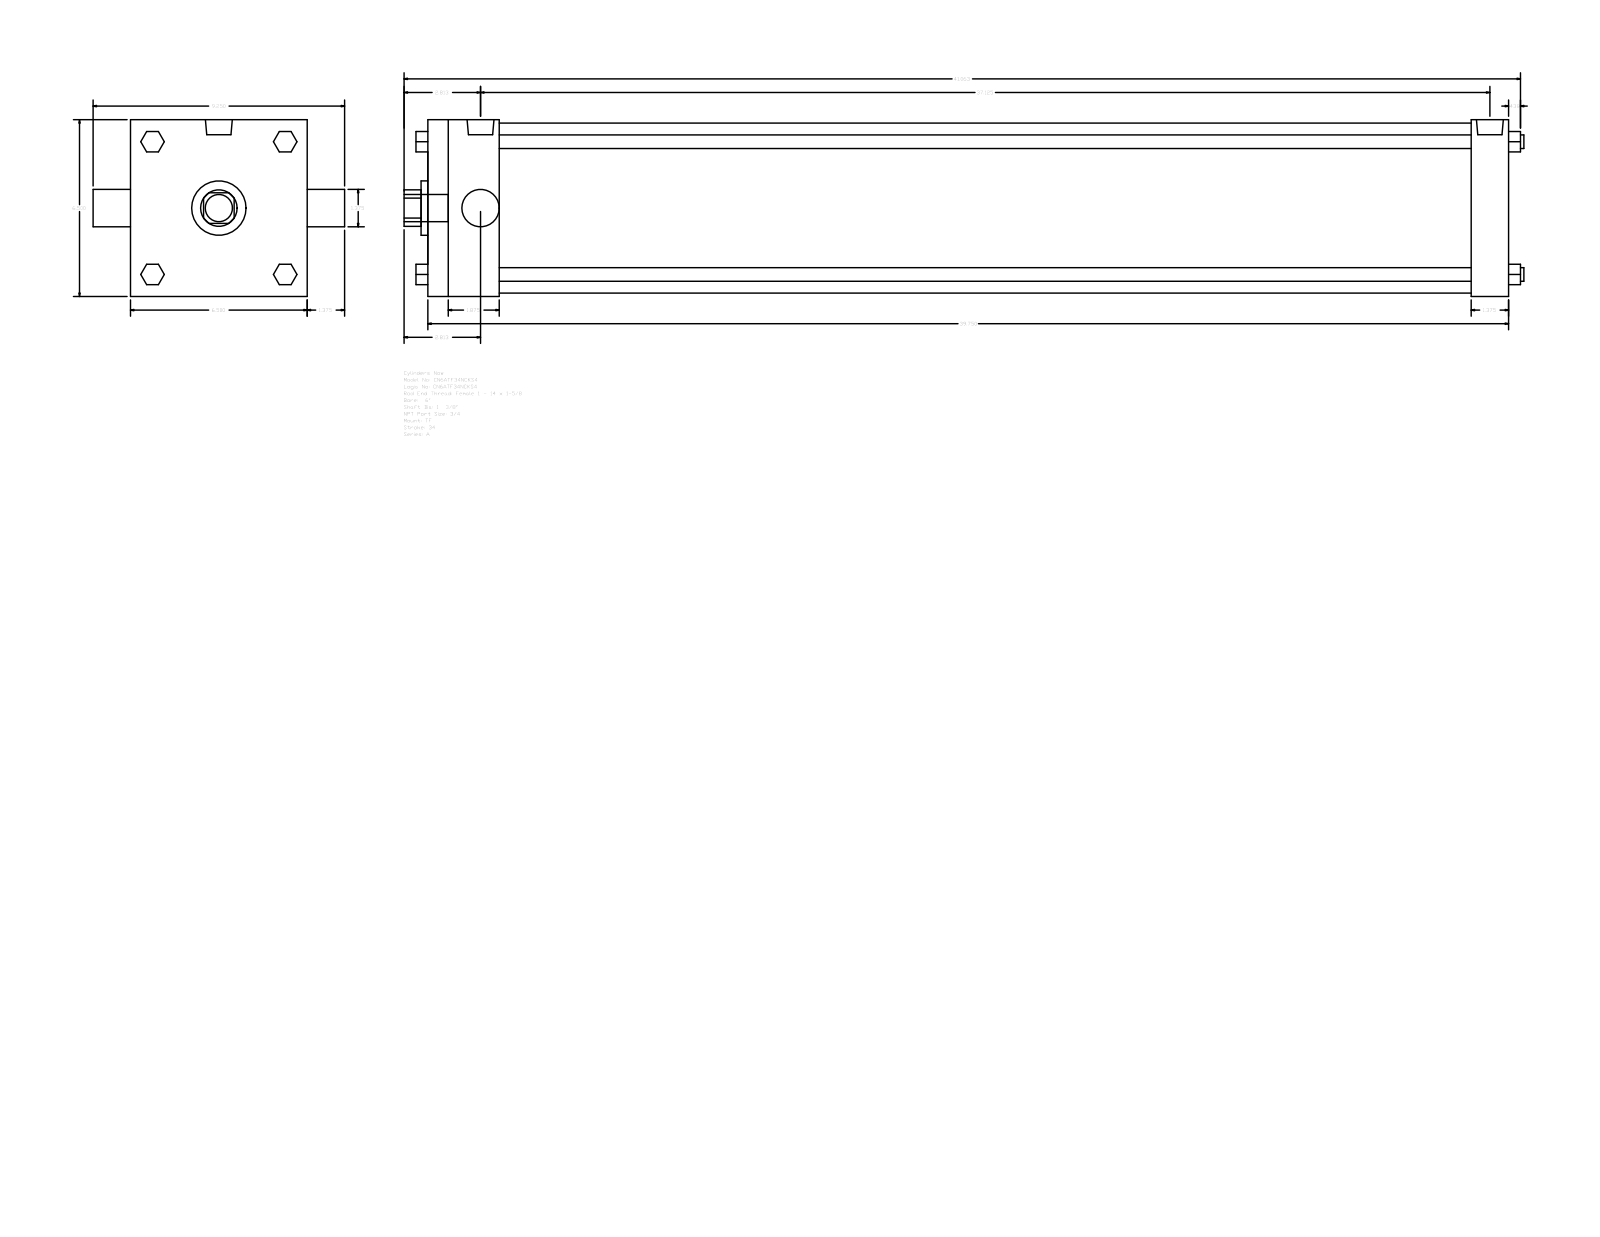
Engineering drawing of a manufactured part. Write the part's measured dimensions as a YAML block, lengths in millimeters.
part_name: "A_TF__0600_1.375"
step_written_by: "GSSL Pune (CONFIG_CONTROL_DESIGN)"
units: millimeters
bodies: {solids: 0, faces: 120, planar: 92, cylindrical: 28, other: 0}
overall_size: [1046.16, 234.95, 165.1]
round_holes:
  - {diameter: 34.92, count: 2}
  - {diameter: 50.8, count: 1}
  - {diameter: 158.75, count: 1}
round_bosses_or_shafts:
  - {diameter: 12.7, count: 4}
  - {diameter: 15.08, count: 3}
  - {diameter: 25.12, count: 2}
  - {diameter: 25.4, count: 1}
partial_cylinders:
  - {radius: 17.06, count: 1}
face_to_face_distances: [165.1, 1009.65, 66.67, 942.98, 974.72, 908.05, 34.93, 19.05, 61.97, 107.34]
